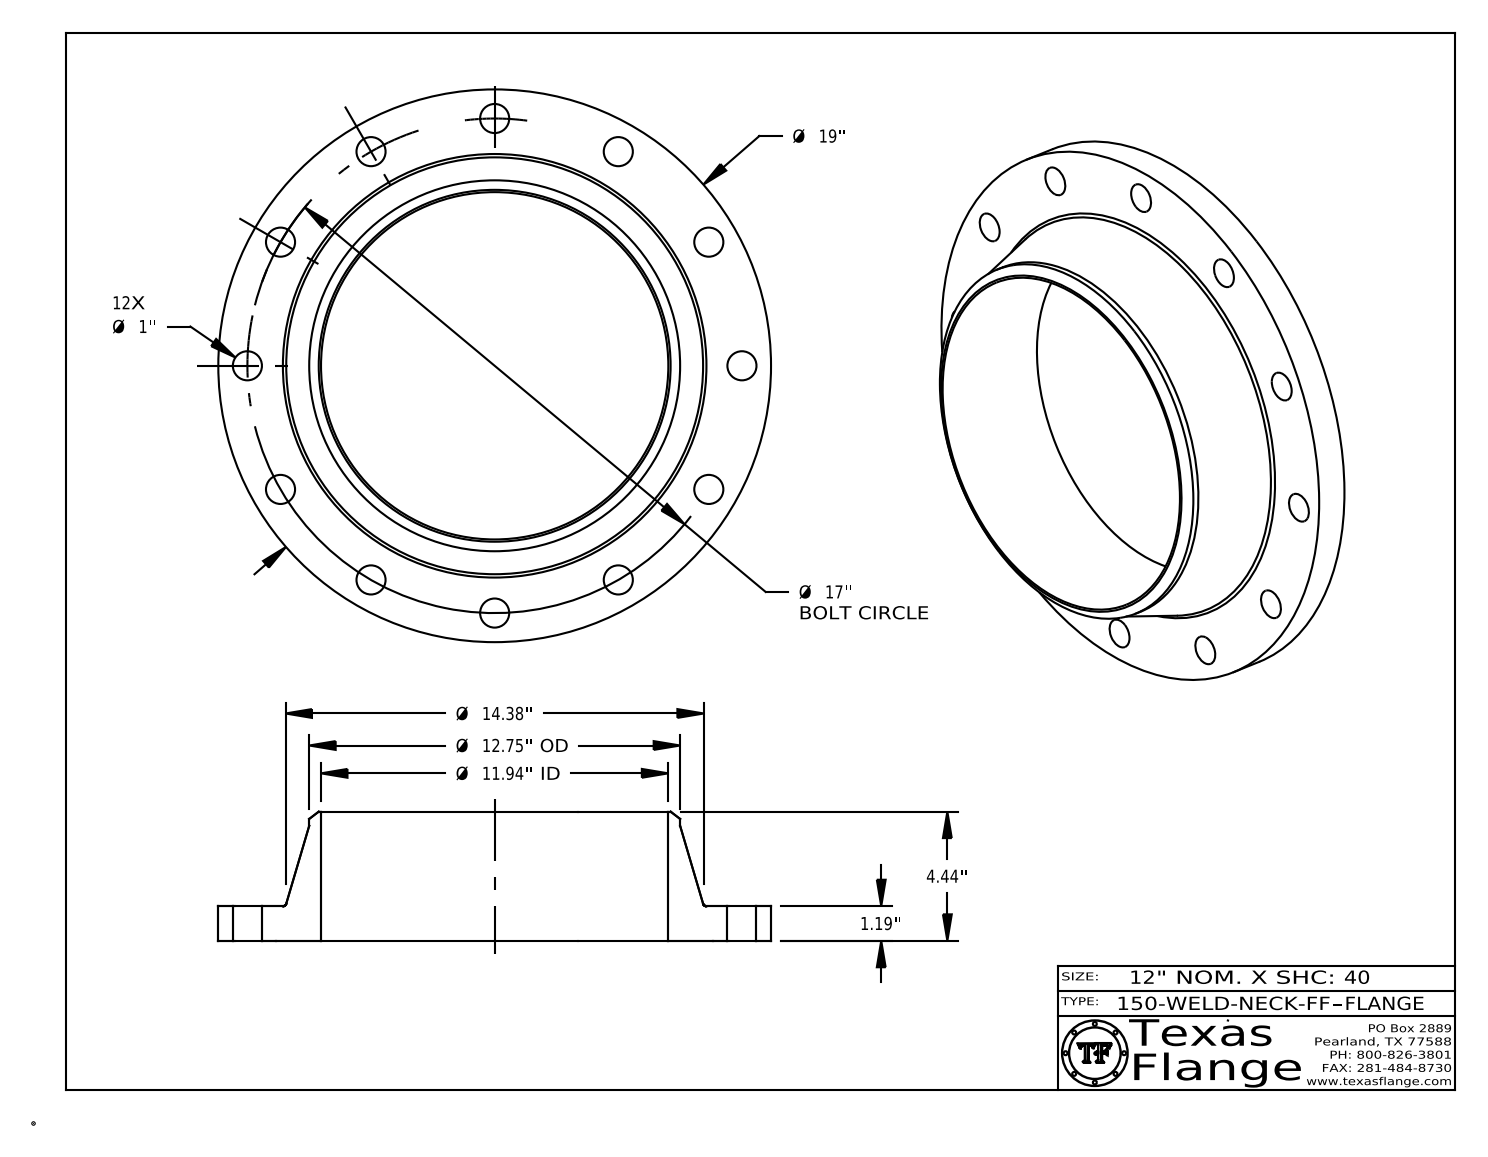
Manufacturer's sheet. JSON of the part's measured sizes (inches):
{"part_name": "150-WELD-NECK-FF", "step_written_by": "CATIA V5 STEP AP214 (AUTOMOTIVE_DESIGN)", "units": "inches", "bodies": {"solids": 1, "faces": 425, "planar": 369, "cylindrical": 50, "other": 6}, "overall_size": [19, 19, 4.44], "volume_in3": 289.6, "surface_area_in2": 706.5, "round_holes": [[1, 12], [0.495, 1], [11.938, 1]], "round_bosses_or_shafts": [[0.03, 8], [19, 1], [12.75, 1], [0.39, 1]], "face_to_face_distances": [1.19, 4.44, 3.25, 0.015, 1.175, 3.265, 0.148, 0.145, 0.027, 0.096], "hole_center_spacings": [8.5, 16.42, 4.4, 12.02, 14.722, 4.4, 12.021, 14.722]}
